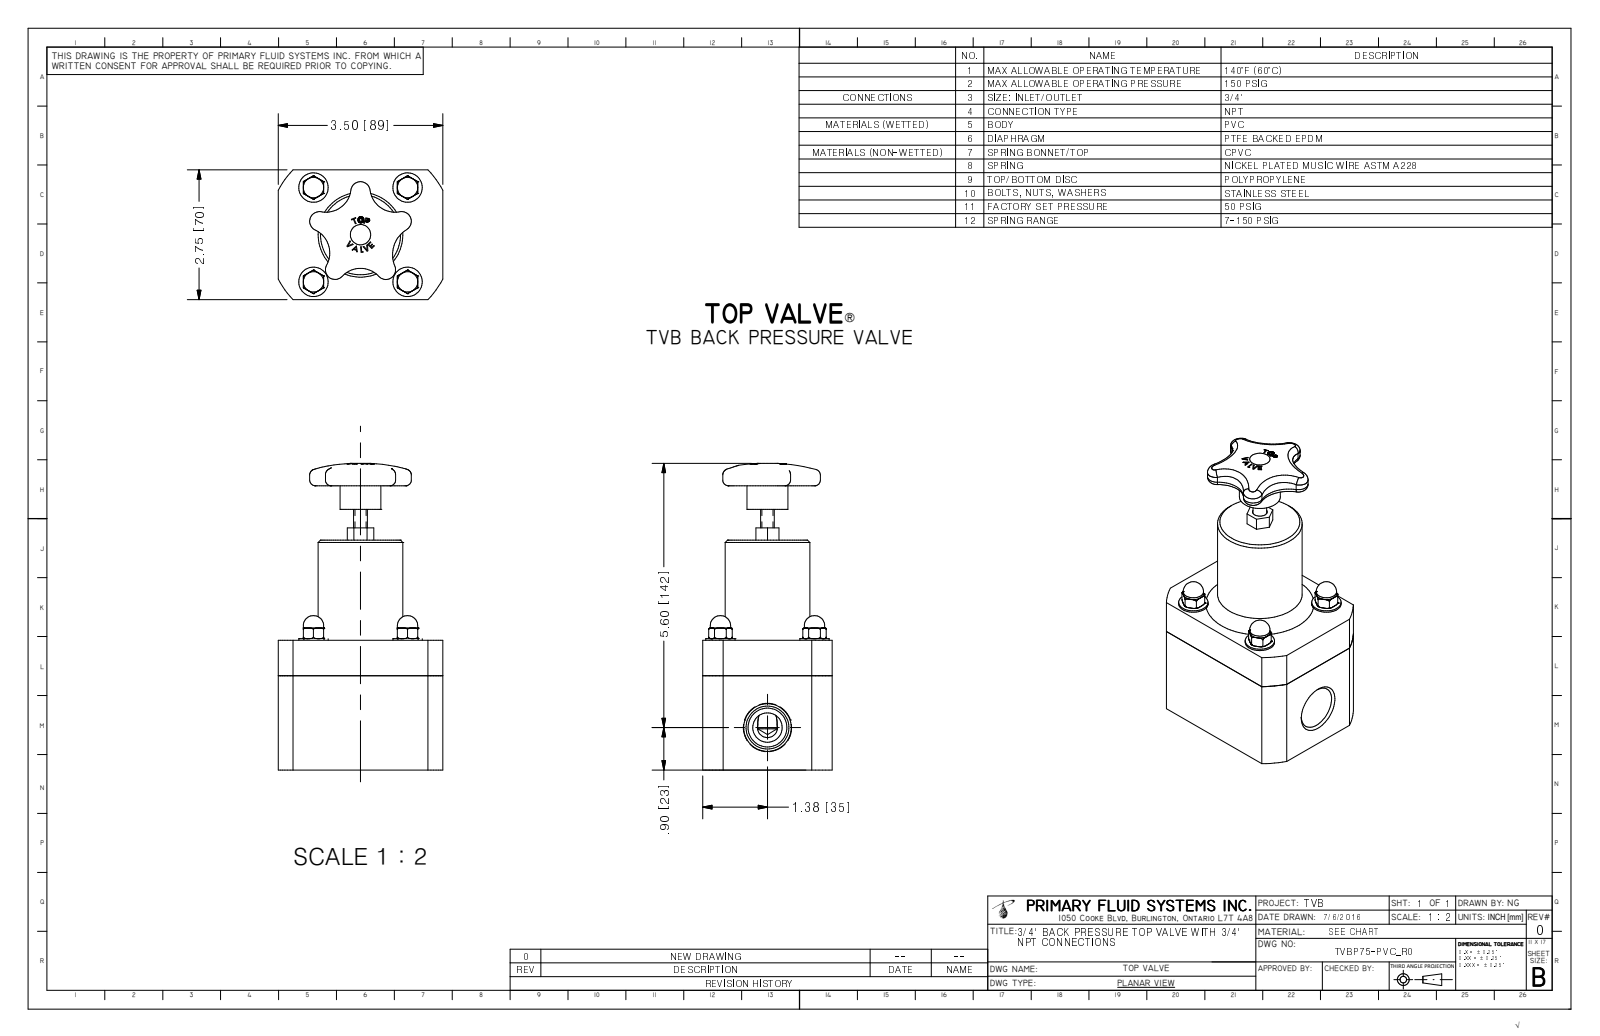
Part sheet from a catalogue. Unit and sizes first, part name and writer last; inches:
Units: inches
Overall size (bounding box): 6.502 × 3.5 × 2.75
Round holes (diameter × count): ⌀0.175 ×4, ⌀0.281 ×1, ⌀0.313 ×1, ⌀0.911 ×1
Round bosses / shafts (diameter × count): ⌀0.625 ×4, ⌀0.433 ×4, ⌀0.375 ×4, ⌀1.8 ×1, ⌀0.87 ×1, ⌀0.293 ×1, ⌀0.25 ×1
Partial cylindrical surfaces — rounded edges, fillets, slot ends (radius × count): R0.085 ×5, R0.205 ×5, R0.536 ×4, R0.656 ×4, R0.625 ×1, R0.745 ×1, R1.988 ×1
Main face-to-face distances: 2.75, 2.75, 3.5, 4.875, 2.125, 0.75, 2, 2.786, 0.036, 2.089
Hole centre spacings: 1.414, 2, 2.828
Volume: 31.75 in³ · Surface area: 86.95 in²
Bodies: 1 solid, 350 faces (148 planar, 49 cylindrical, 153 other)
Part name (STEP PRODUCT): TVBP75-PVC_R0
STEP written by: Autodesk Inventor 2009 (AUTOMOTIVE_DESIGN)
